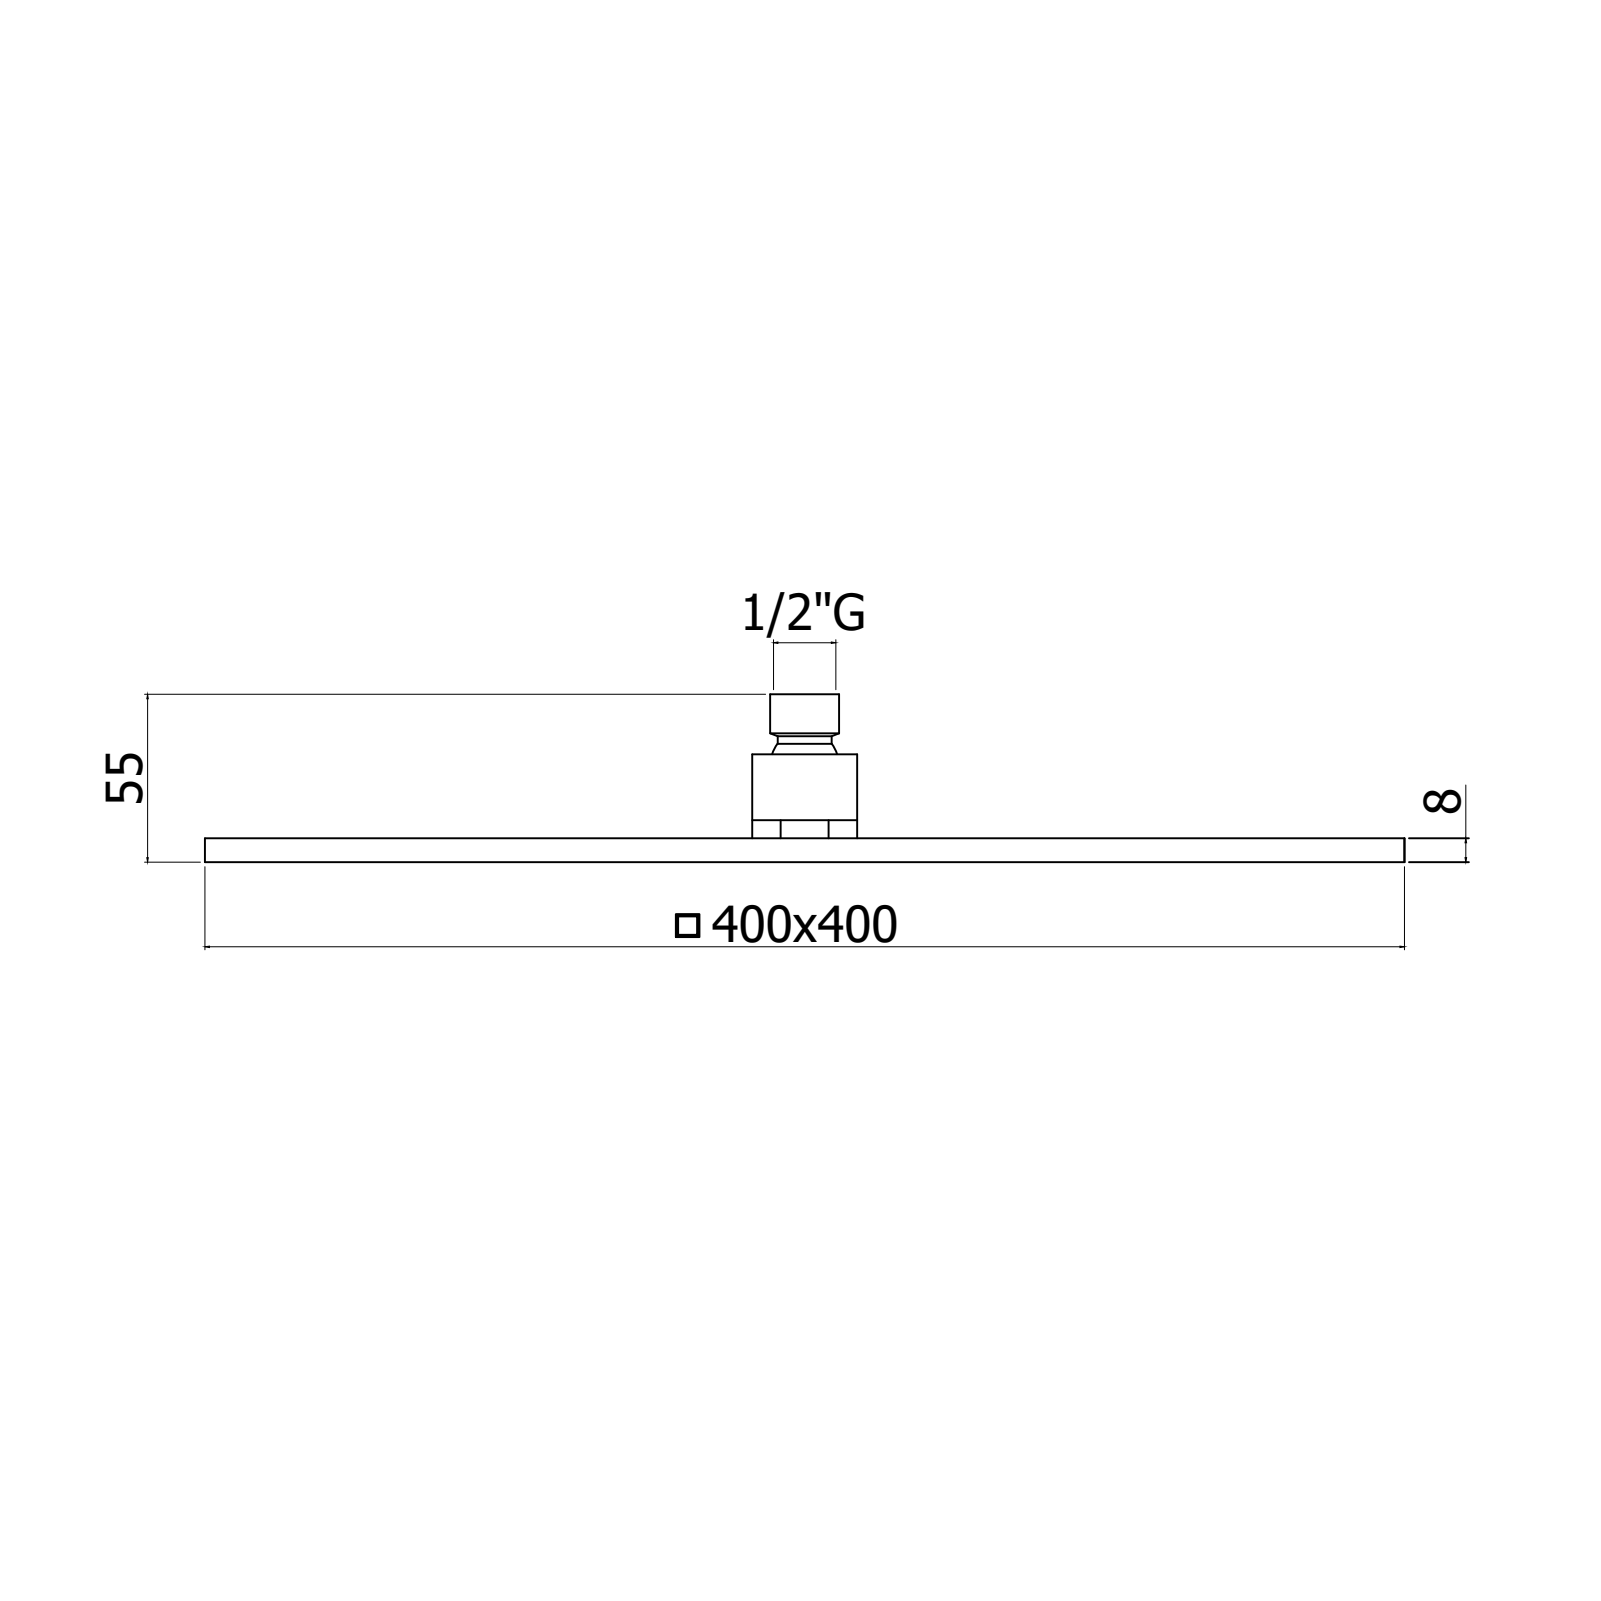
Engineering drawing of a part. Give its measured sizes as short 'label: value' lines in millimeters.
name: 4071454CR
written by: CREO PARAMETRIC BY PTC INC, 2020044 (CONFIG_CONTROL_DESIGN)
unit: mm
bodies: 1 solid, 6724 faces (861 planar, 1636 cylindrical, 4227 other)
size: 400.2 × 400.2 × 51.9
volume: 618 420 mm³; area: 643 885 mm²
holes: 196× ⌀1.5, 196× ⌀1.7, 29× ⌀7, 28× ⌀2.5, 28× ⌀5.1, 28× ⌀6, 1× ⌀15, 1× ⌀16, 1× ⌀16.5, 1× ⌀18.63, 1× ⌀23.8, 1× ⌀24
bosses: 196× ⌀10, 28× ⌀5, 1× ⌀31.8, 1× ⌀29.4, 1× ⌀28, 1× ⌀23.2
rounds: 14× R20, 8× R1, 4× R12
face distances: 8.5, 7.5, 1, 1.5, 6, 7, 5.6, 2.9, 1.4, 4.6
hole spacings: 58.6, 386.47, 117.2, 399.57, 175.8, 420.51, 382, 234.4
